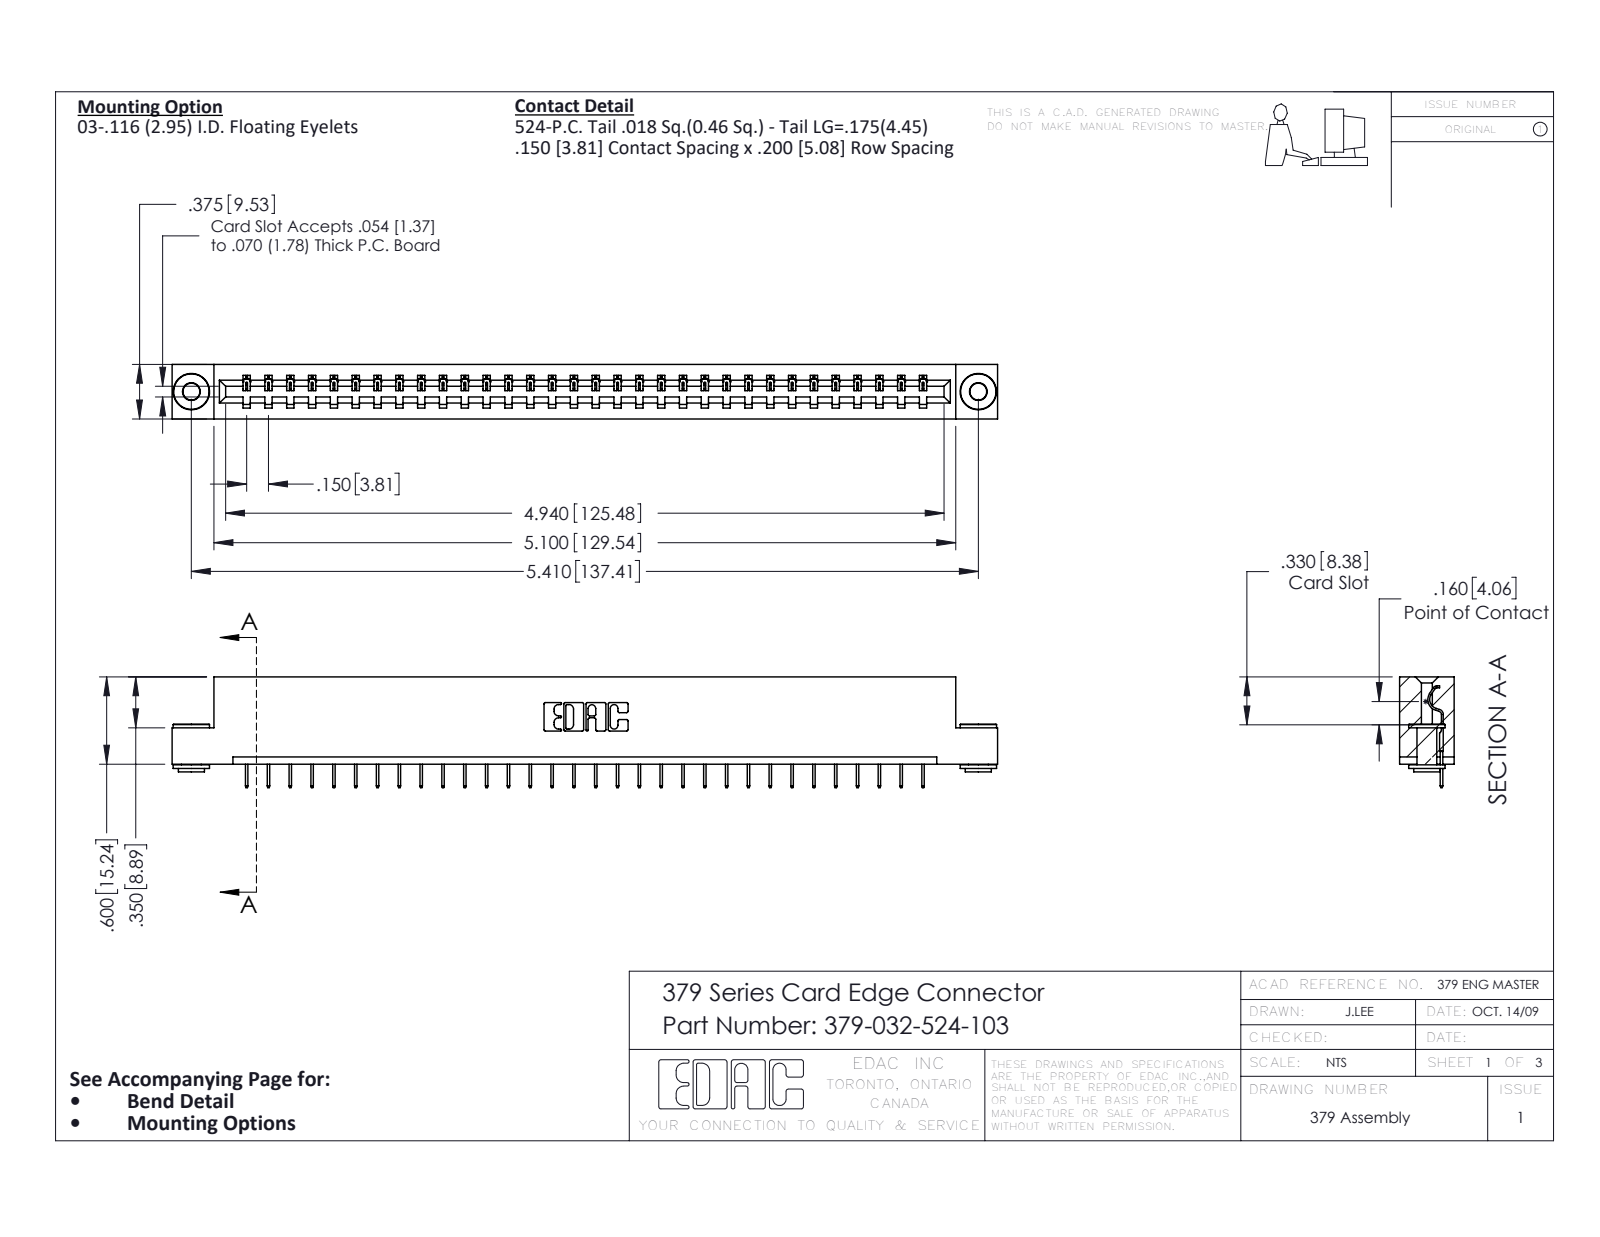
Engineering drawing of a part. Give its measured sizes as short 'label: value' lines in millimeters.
name: 345-250-002_345-250-002-102; 379 Part_Flush - .156 Dia - TH; 379-032-524-103; 345-292-001_345-293-124
written by: SolidWorks 2016 (CONFIG_CONTROL_DESIGN)
unit: mm
bodies: 35 solids, 2136 faces (1616 planar, 512 cylindrical, 8 other)
size: 144.1 × 19.4 × 9.5
volume: 14 900 mm³; area: 15 000 mm²
holes: 2× ⌀2.9, 2× ⌀4
bosses: 2× ⌀6.4, 2× ⌀4.6, 2× ⌀3.5
rounds: 64× R0.2, 22× R0.3, 6× R0.2, 6× R0.8, 3× R0.7, 1× R0.4, 1× R0.6, 1× R0.6
face distances: 7.6, 1.9, 9.5, 5.7, 15.2, 5.1, 14, 7, 3.8, 3.8
hole spacings: 137.4
